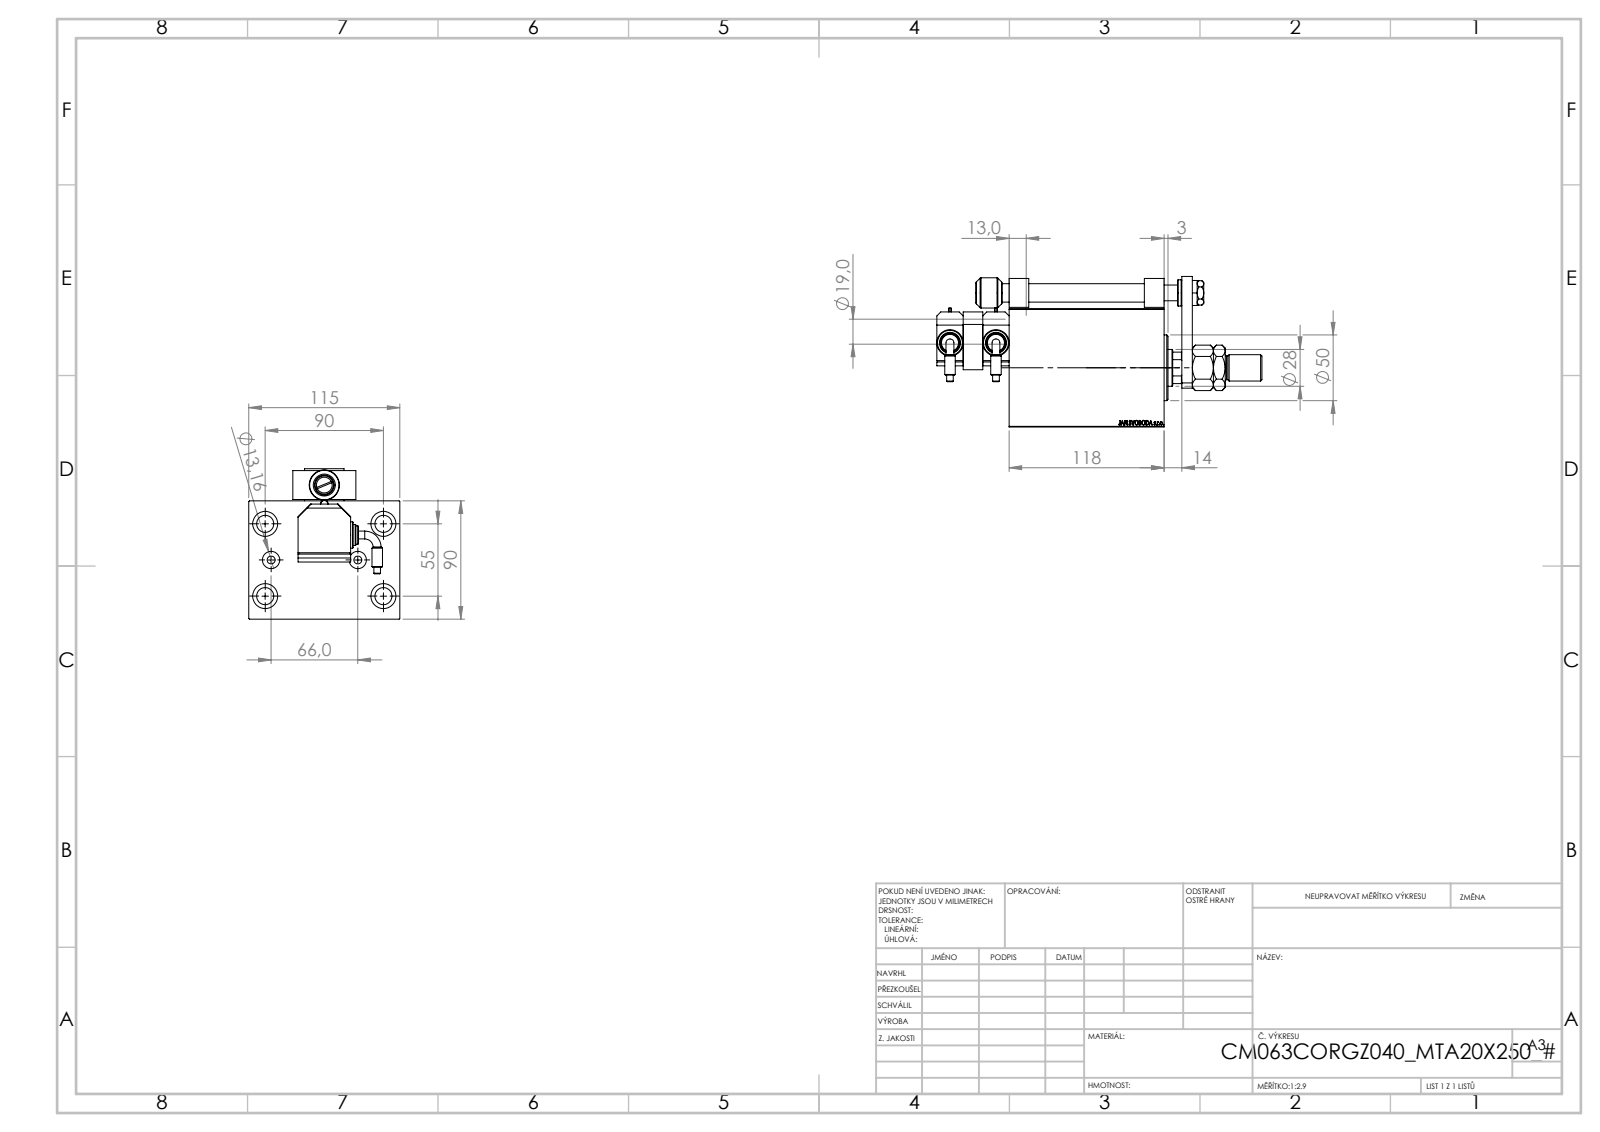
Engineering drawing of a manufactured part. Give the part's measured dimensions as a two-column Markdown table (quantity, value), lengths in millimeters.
| quantity | value |
| --- | --- |
| part name | NUT_D16; NUT_D19_P; TYC_P; V450CM_C_Body (+7 more) |
| STEP written by | SolidWorks 2019 (CONFIG_CONTROL_DESIGN) |
| units | millimeters |
| bodies | 15 solids, 1163 faces (540 planar, 128 cylindrical, 495 other) |
| overall size | 247.5 × 115 × 114.5 |
| volume | 1 233 000 mm³ |
| surface area | 190 466 mm² |
| round holes (diameter × count) | 13 × 5, 4 × 4, 8 × 4, 19 × 4, 6 × 2, 13.16 × 2, 12 × 1, 14 × 1, 16.5 × 1, 18.5 × 1, 28 × 1, 31.5 × 1 |
| round bosses / shafts (diameter × count) | 20 × 4, 16 × 2, 14 × 2, 8 × 2, 6 × 2, 5.04 × 2, 50 × 1, 23 × 1 |
| partial cylindrical surfaces (radius × count) | 3 × 1, 13.5 × 1 |
| main face-to-face distances | 90, 115, 35, 118, 46, 72, 5, 15, 20, 103 |
| hole center spacings | 30, 52.74, 82.71, 20, 33, 53.81, 55, 65.86 |
